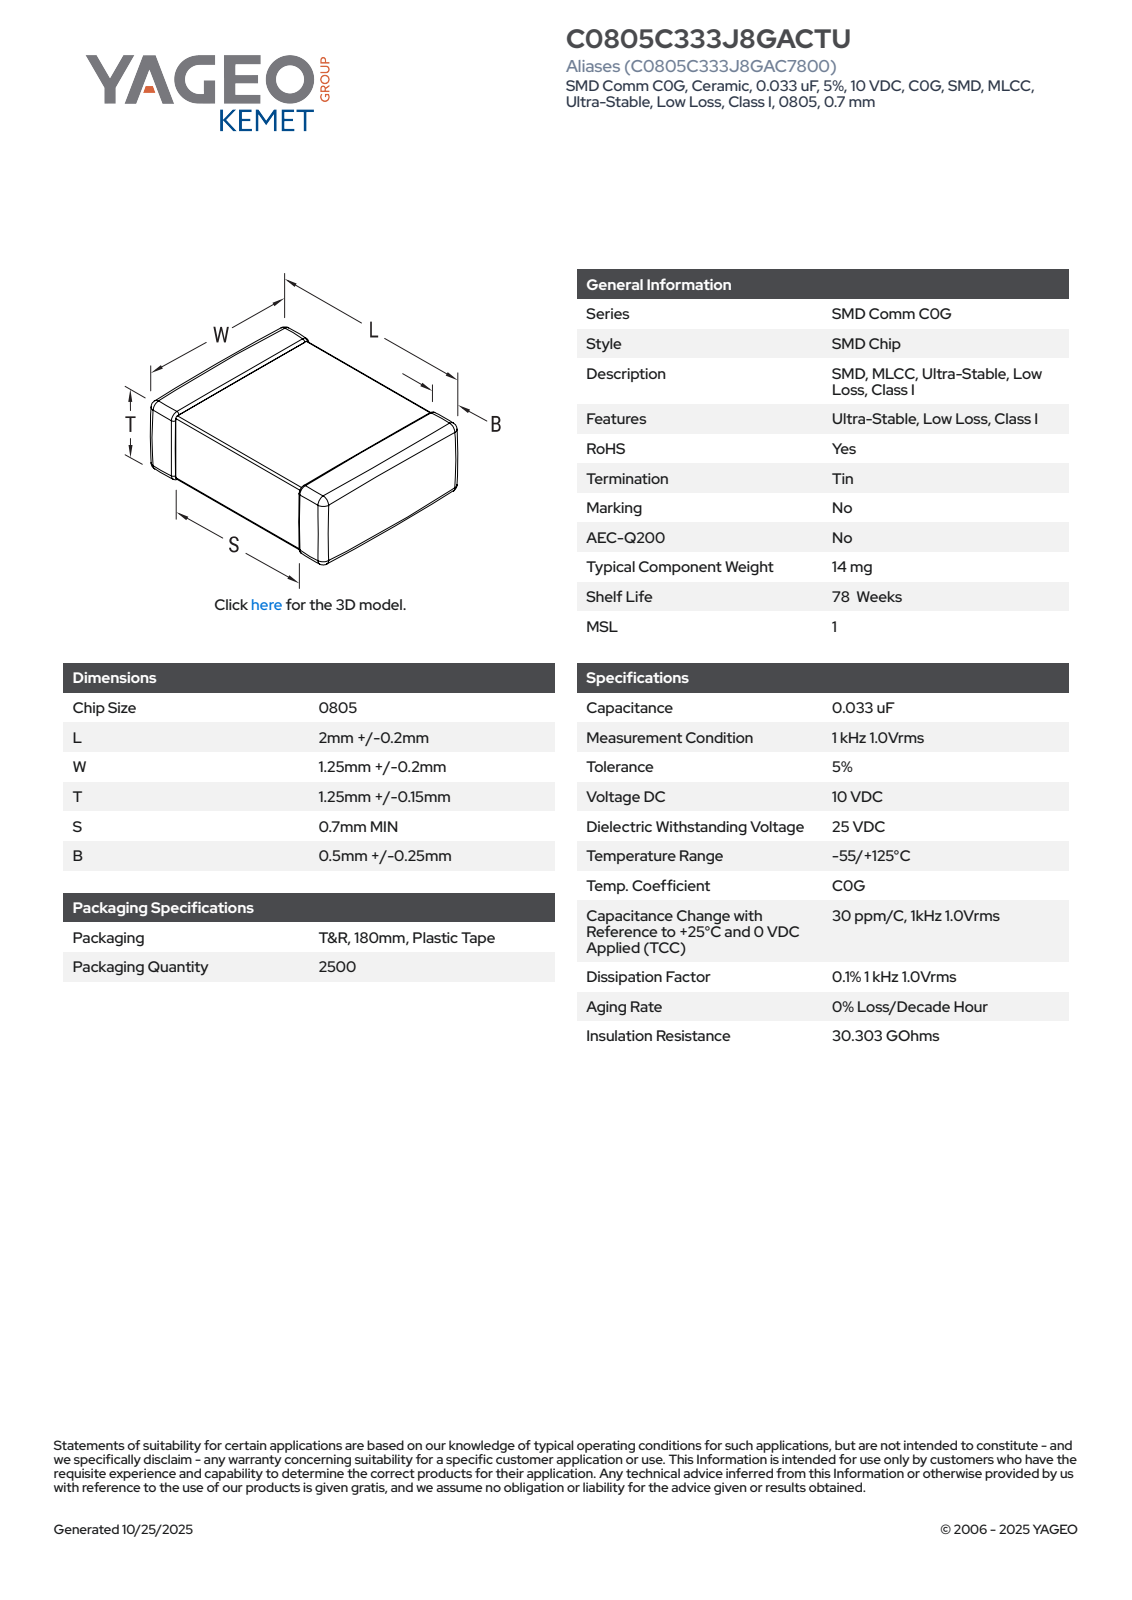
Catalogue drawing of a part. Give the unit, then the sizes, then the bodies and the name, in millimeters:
Units: millimetres
Overall size (bounding box): 2.2 × 1.45 × 1.4
Main face-to-face distances: 1.37, 1.4, 2.2, 1.45, 1.42, 1.34, 1.39, 0.97, 1.23, 1.19
Volume: 4 mm³ · Surface area: 17 mm²
Bodies: 4 solids, 121 faces (71 planar, 34 cylindrical, 16 other)
Part name (STEP PRODUCT): CCS_CCSTD_0805_L2.2W1.45T1.4B0.5
STEP written by: SolidWorks 2021 (AUTOMOTIVE_DESIGN)
